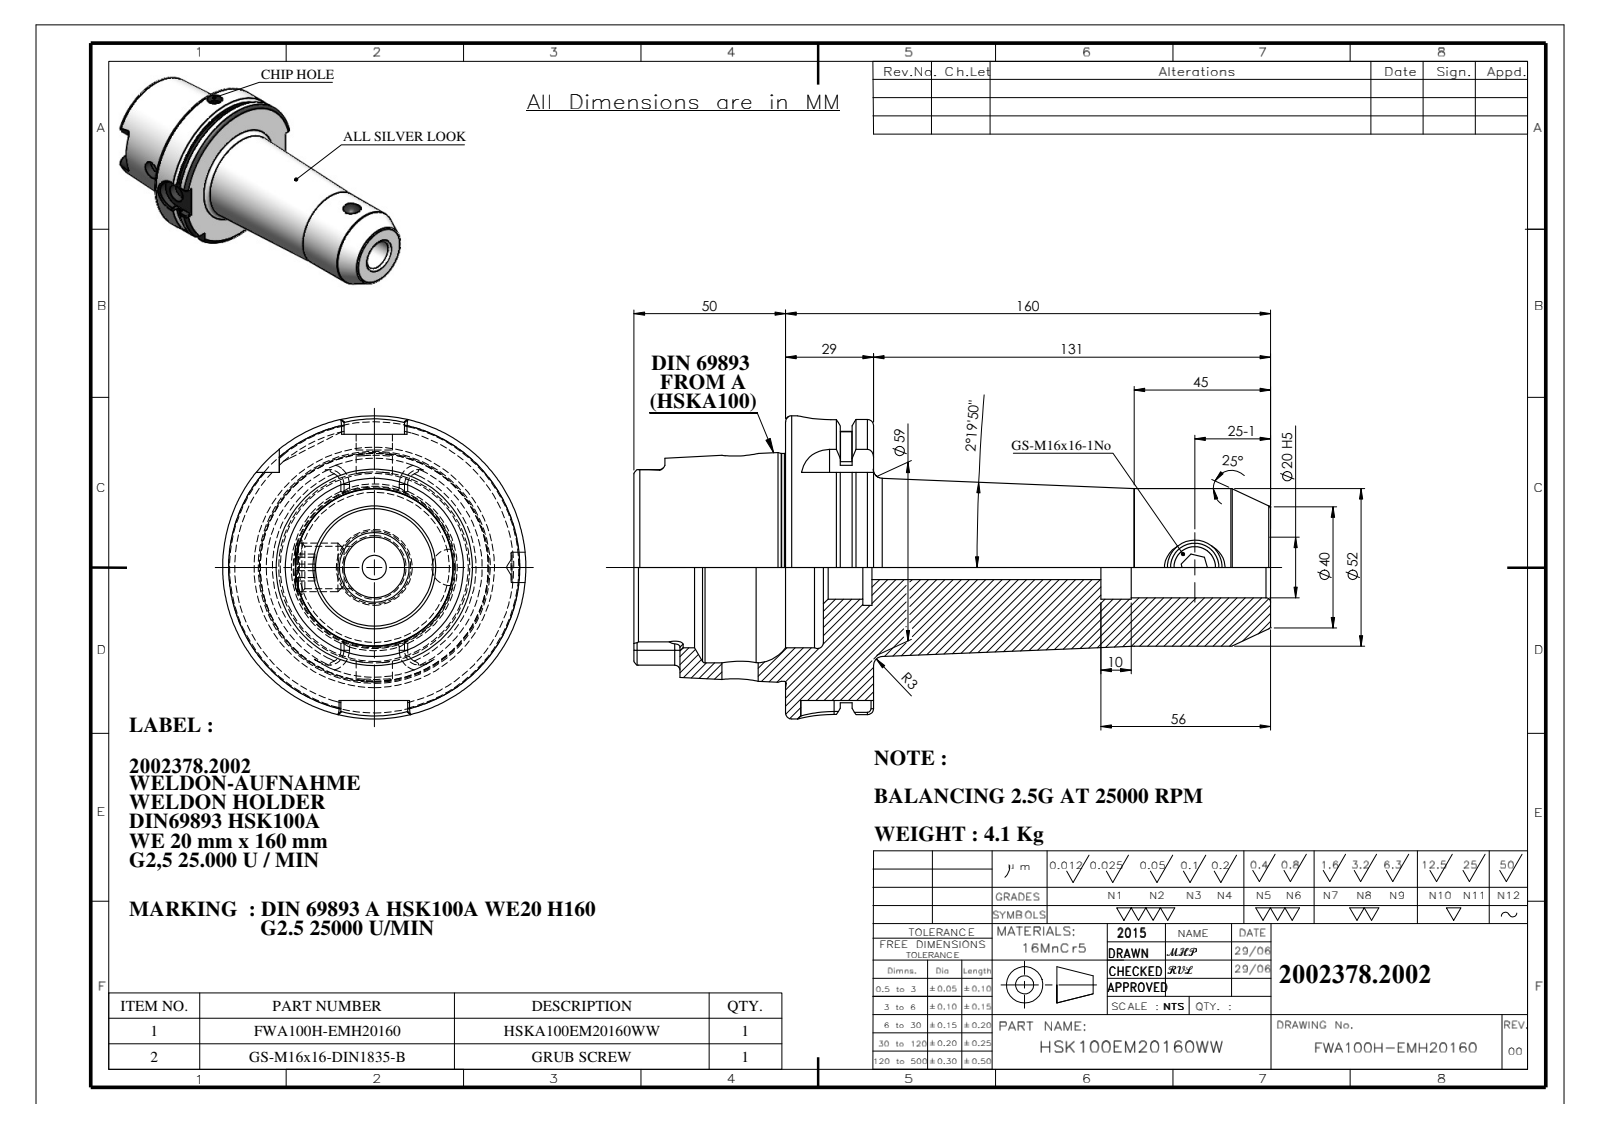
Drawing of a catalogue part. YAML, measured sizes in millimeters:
part_name: "GS-M16X16-DIN1835-B_ISO 4026 - M16 x 10-N; 91100A-WE820160; HSKA100EM20160WW"
step_written_by: "SolidWorks 2018 (CONFIG_CONTROL_DESIGN)"
units: millimeters
bodies: {solids: 2, faces: 209, planar: 64, cylindrical: 58, other: 87}
overall_size: [210, 100, 100]
volume: 529762
surface_area: 77474
round_holes:
  - {diameter: 12, count: 2}
  - {diameter: 8, count: 1}
  - {diameter: 10, count: 1}
  - {diameter: 14, count: 1}
  - {diameter: 18, count: 1}
  - {diameter: 20, count: 1}
  - {diameter: 21, count: 1}
  - {diameter: 25, count: 1}
  - {diameter: 53, count: 1}
  - {diameter: 63, count: 1}
round_bosses_or_shafts:
  - {diameter: 100, count: 1}
  - {diameter: 92, count: 1}
  - {diameter: 75.16, count: 1}
  - {diameter: 52, count: 1}
  - {diameter: 16, count: 1}
partial_cylinders:
  - {radius: 1.8, count: 6}
  - {radius: 4.88, count: 4}
  - {radius: 10, count: 2}
  - {radius: 11, count: 1}
face_to_face_distances: [29, 12.5, 16.5, 50, 62.5, 79, 210, 160, 147.5, 131]
hole_center_spacings: [30, 128]
